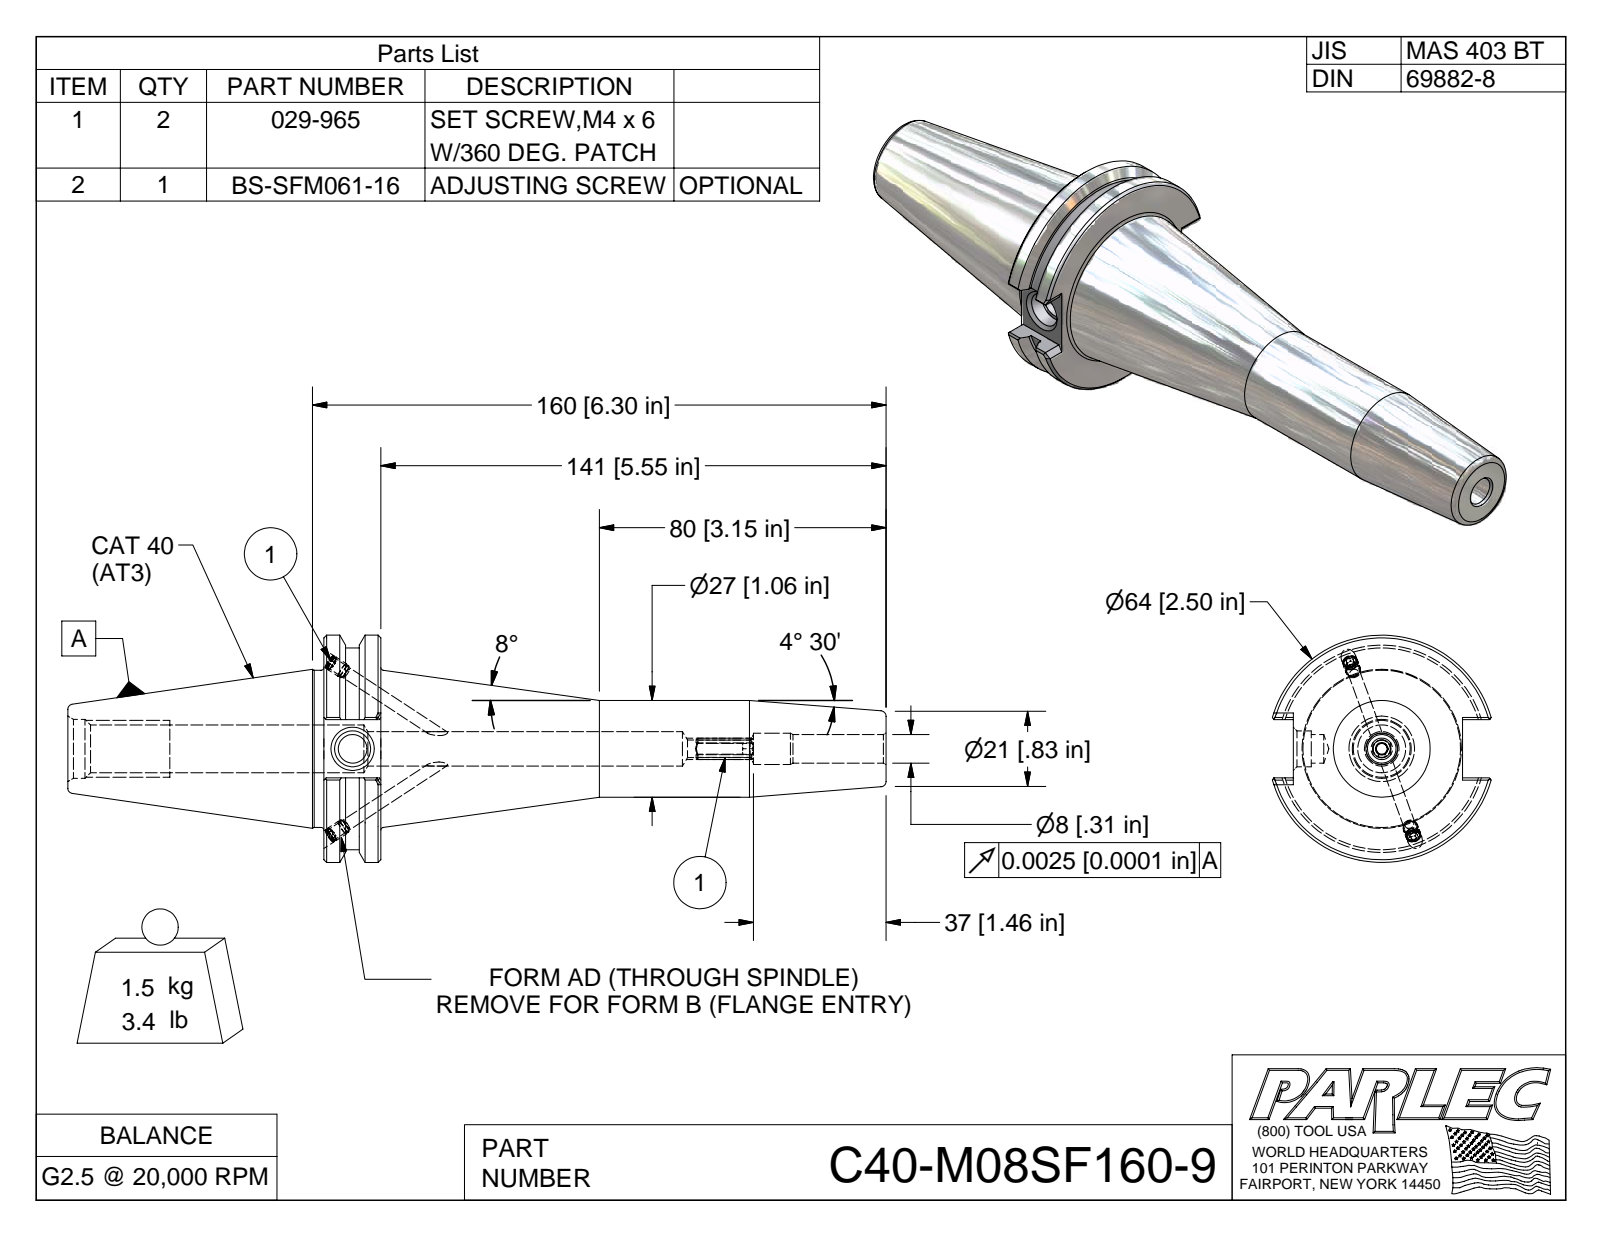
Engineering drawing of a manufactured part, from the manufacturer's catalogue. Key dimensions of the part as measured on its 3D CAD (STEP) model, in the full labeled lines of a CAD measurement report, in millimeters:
Part name (STEP PRODUCT): C40-M08SF160-9; C40BC-M08SF160-9-1; 029-965; BS-SFM061-16
STEP written by: Autodesk Inventor 2009 (AUTOMOTIVE_DESIGN)
Units: millimetres
Bodies: 4 solids, 138 faces (65 planar, 22 cylindrical, 51 other)
Overall size (bounding box): 228.3 × 63.5 × 61
Volume: 194 800 mm³ · Surface area: 37 670 mm²
Round holes (diameter × count): ⌀3.3 ×2, ⌀4.1 ×2, ⌀8 ×1, ⌀8.7 ×1
Round bosses / shafts (diameter × count): ⌀4.2 ×2, ⌀4 ×2, ⌀63.5 ×1, ⌀56.4 ×1, ⌀43.9 ×1, ⌀27 ×1
Partial cylindrical surfaces — rounded edges, fillets, slot ends (radius × count): R3 ×1
Main face-to-face distances: 15.9, 156.8, 141, 16.3, 47.2, 71.4, 87.3, 228.3, 81.3, 9.9
